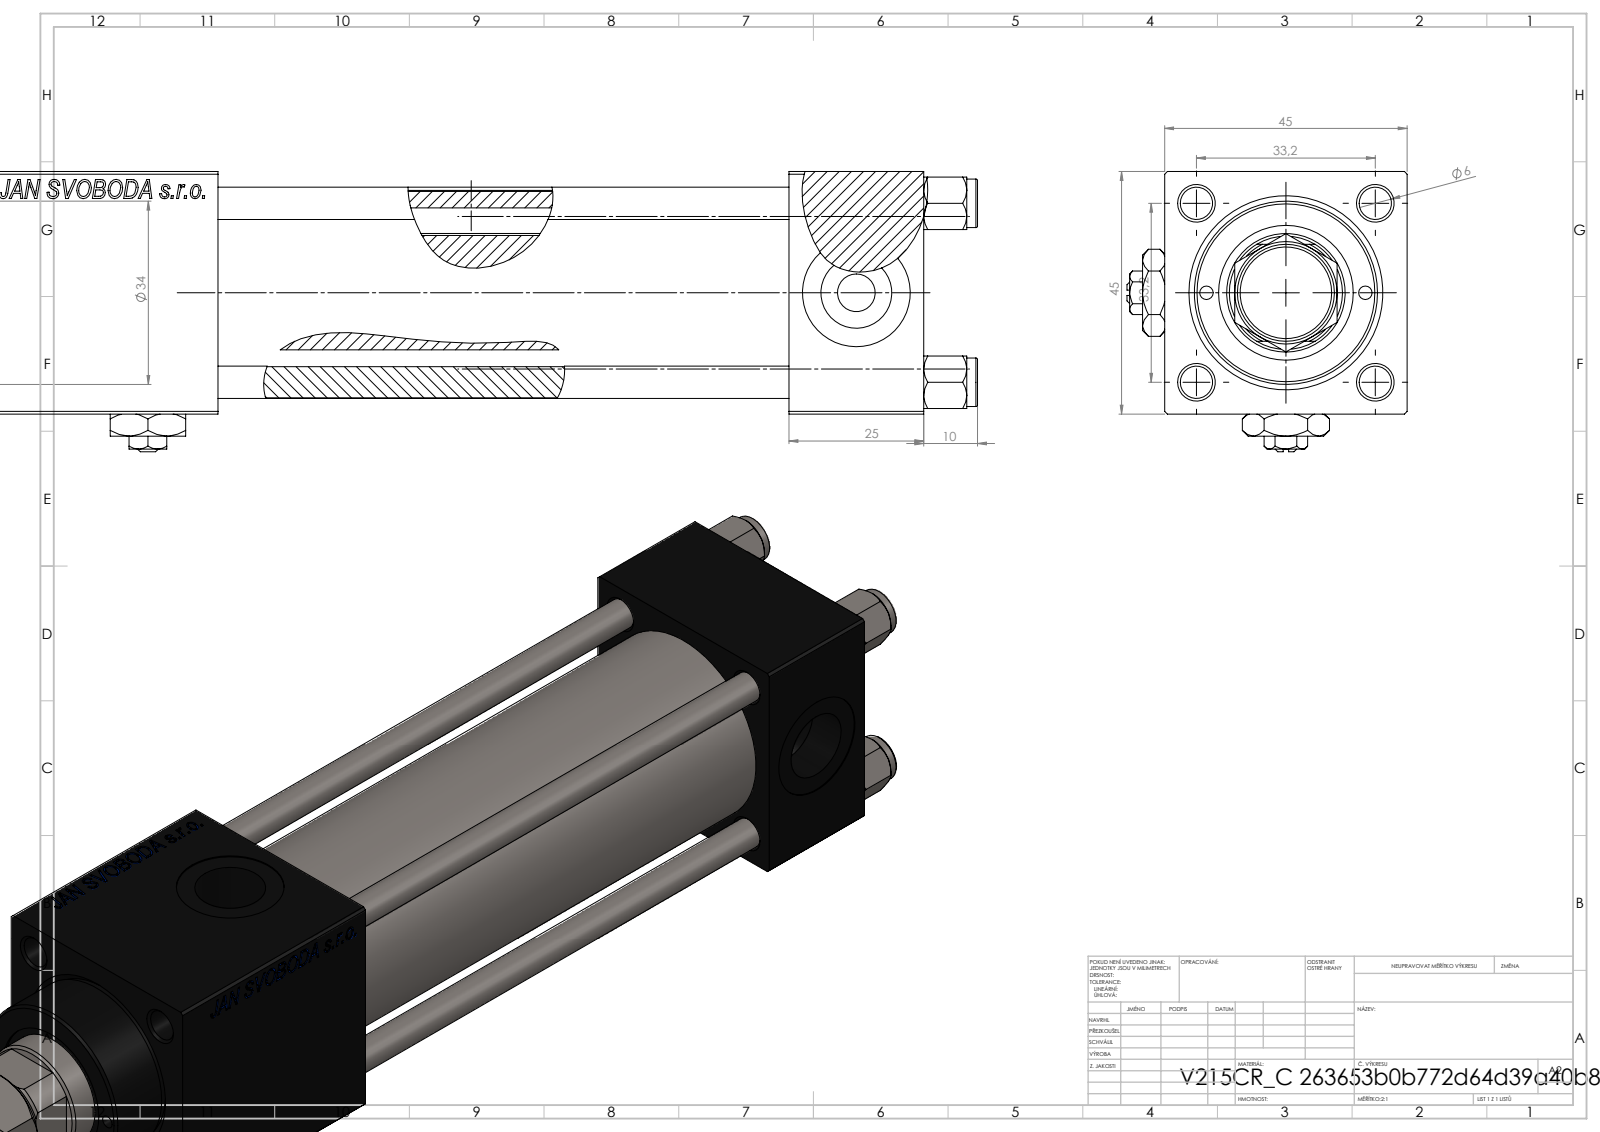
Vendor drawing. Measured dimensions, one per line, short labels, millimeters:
name: NUT_M5_C; V215CR_C_TYCINKA; V215CR_C_Body; V215CR_VCP_C (+3 more)
written by: SolidWorks 2019 (CONFIG_CONTROL_DESIGN)
unit: mm
bodies: 14 solids, 1306 faces (590 planar, 106 cylindrical, 610 other)
size: 247 × 52 × 52
volume: 262 300 mm³; area: 96 515 mm²
holes: 4× ⌀6, 2× ⌀2.5, 2× ⌀7, 2× ⌀13.16, 2× ⌀20, 1× ⌀10.5, 1× ⌀22, 1× ⌀24, 1× ⌀25, 1× ⌀32, 1× ⌀33
bosses: 4× ⌀9, 1× ⌀38, 1× ⌀34, 1× ⌀18, 1× ⌀11
rounds: 1× R10.5
face distances: 45, 25, 179, 106, 131, 154, 44.8, 13, 48, 150.3
hole spacings: 16.7, 23.48, 33.2, 35.47, 14.75, 46.95, 29.5
